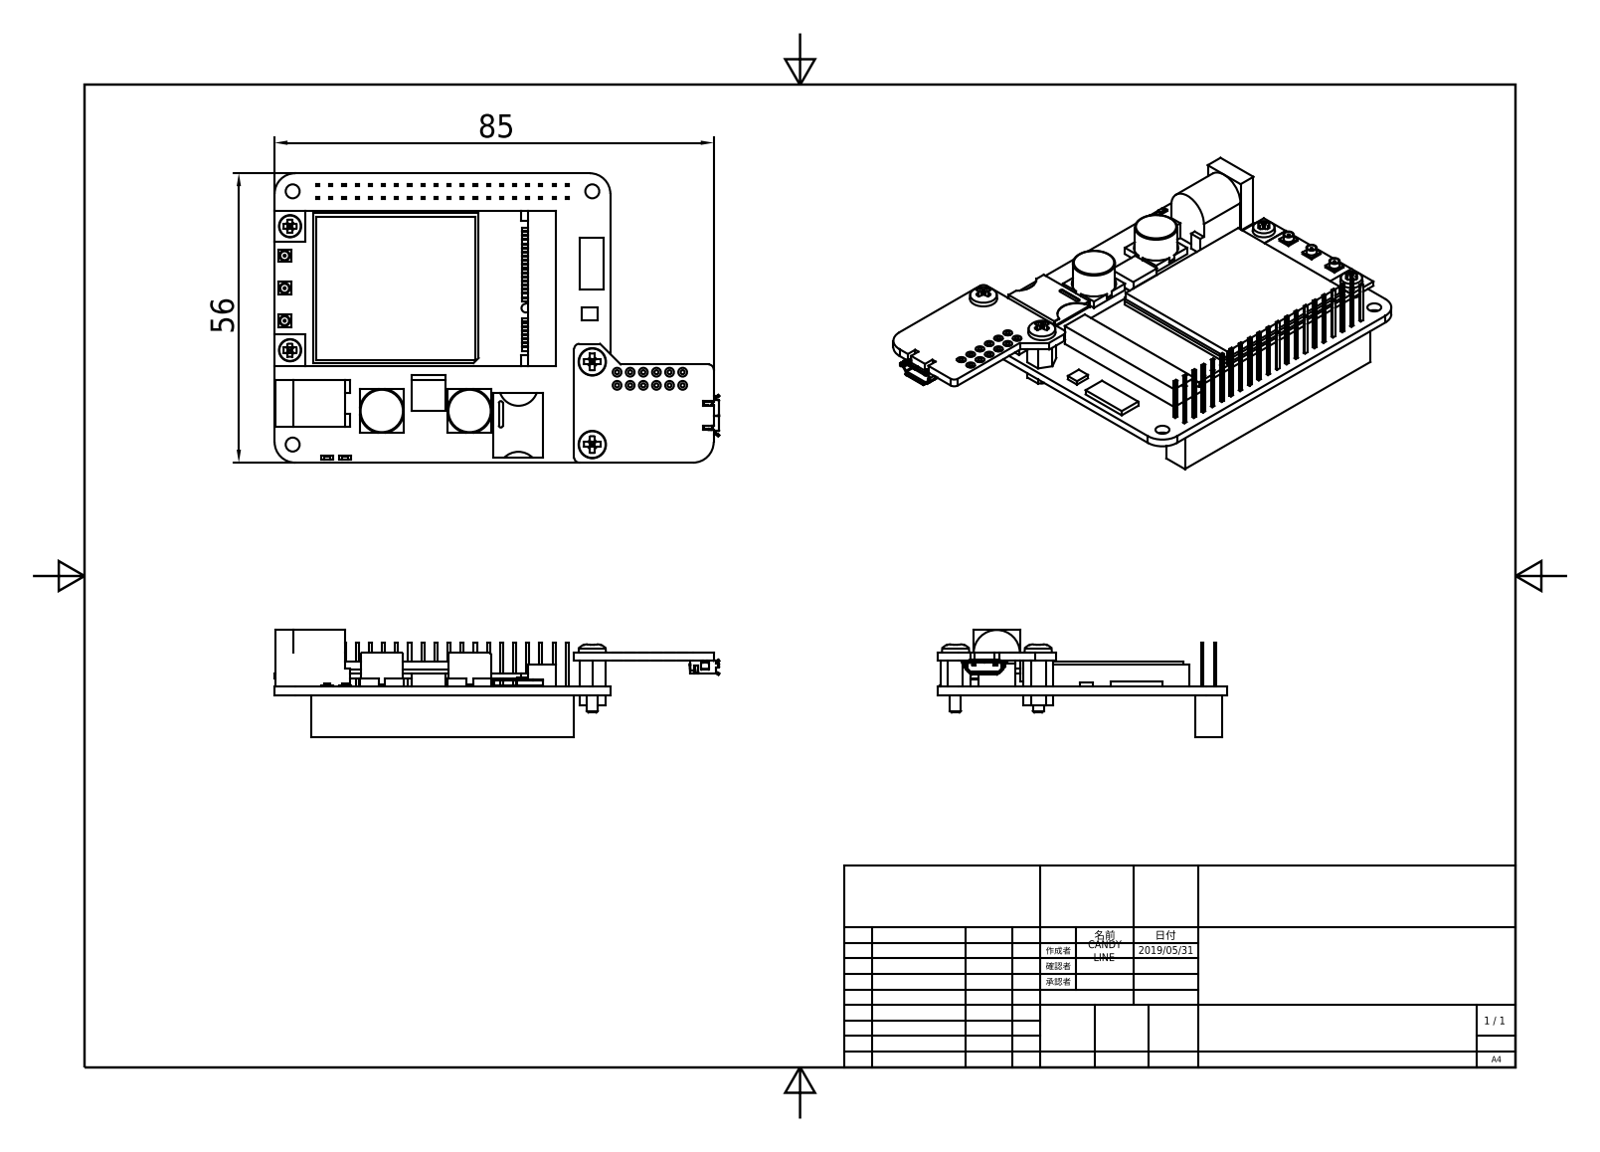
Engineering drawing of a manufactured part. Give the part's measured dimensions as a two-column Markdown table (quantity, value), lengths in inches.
| quantity | value |
| --- | --- |
| part name | CANDY Pi Lite_拡張基板あり; CANDY Pi Lite Rev3; EC21-J; 拡張基板 (+5 more) |
| STEP written by | Autodesk Inventor 2017 (AUTOMOTIVE_DESIGN) |
| units | inches |
| bodies | 11 solids, 1512 faces (1207 planar, 265 cylindrical, 40 other) |
| overall size | 3.39 × 2.205 × 0.821 |
| volume | 0.947 in³ |
| surface area | 27.73 in² |
| round holes (diameter × count) | 0.031 × 12, 0.106 × 5, 0.067 × 3, 0.016 × 2, 0.062 × 2, 0.102 × 2, 0.339 × 2, 0.083 × 1, 0.248 × 1 |
| round bosses / shafts (diameter × count) | 0.067 × 12, 0.079 × 3, 0.016 × 3, 0.323 × 2, 0.157 × 2, 0.083 × 1, 0.083 × 1 |
| partial cylindrical surfaces (radius × count) | 0.004 × 28, 0.012 × 25, 0.024 × 15, 0.006 × 12, 0.008 × 12, 0.01 × 10, 0.016 × 7, 0.02 × 7 |
| main face-to-face distances | 0.063, 0.059, 0.122, 0.13, 0.26, 0.098, 0.161, 0.189, 0.252, 0.039 |
| hole center spacings | 0.1, 0.141, 0.2, 0.224, 0.3, 0.316, 0.4, 0.412 |
